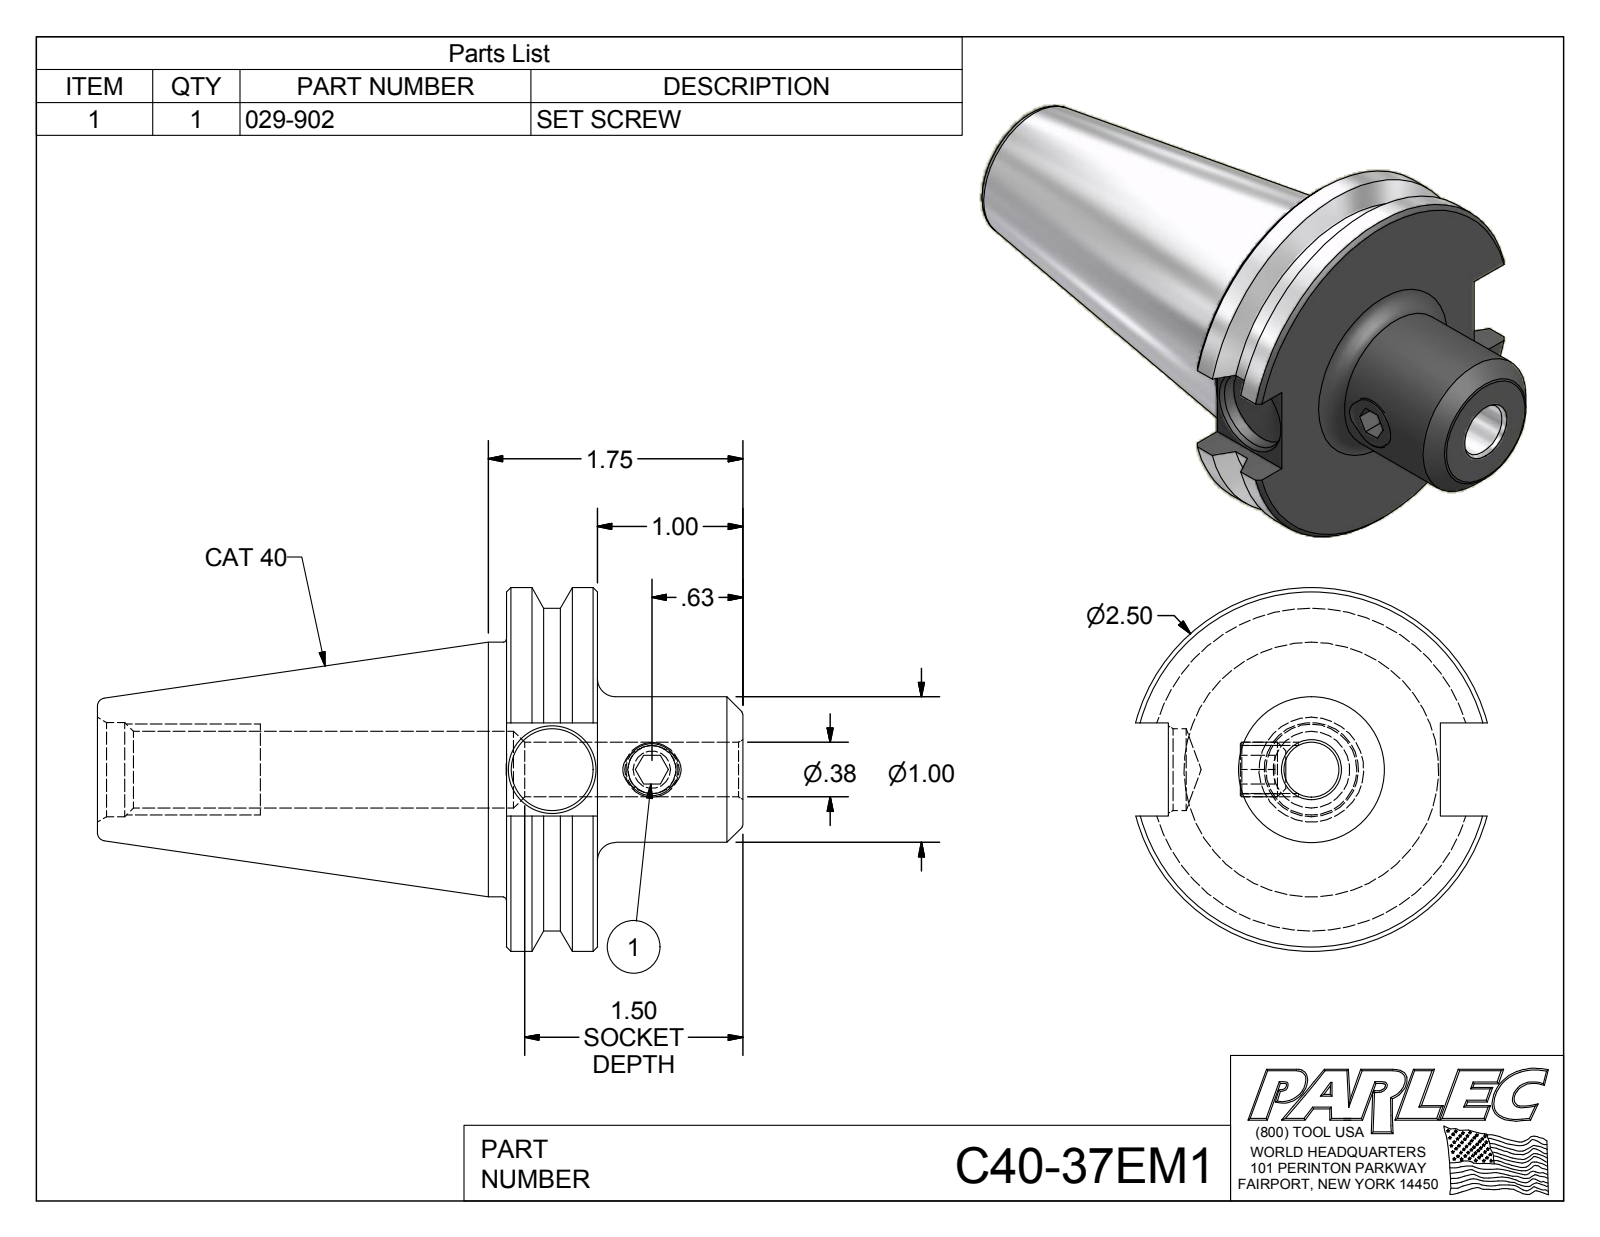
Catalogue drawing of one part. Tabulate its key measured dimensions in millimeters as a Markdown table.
| quantity | value |
| --- | --- |
| part name | C40-37EM1; C40-37EM1-1; 029-902 |
| STEP written by | Autodesk Inventor 2012 (AUTOMOTIVE_DESIGN) |
| units | millimeters |
| bodies | 2 solids, 57 faces (19 planar, 14 cylindrical, 24 other) |
| overall size | 112.7 × 63.5 × 61.4 |
| volume | 112 400 mm³ |
| surface area | 23 050 mm² |
| round holes (diameter × count) | 8.4 × 1, 9.5 × 1, 13.4 × 1, 14.3 × 1, 16.5 × 1 |
| round bosses / shafts (diameter × count) | 63.5 × 1, 56.4 × 1, 44.5 × 1, 25.4 × 1, 9.5 × 1 |
| main face-to-face distances | 15.9, 41.3, 25.4, 16.3, 71.5, 87.3, 112.7, 47.5, 5, 34.9 |
| hole center spacings | 17.4 |
